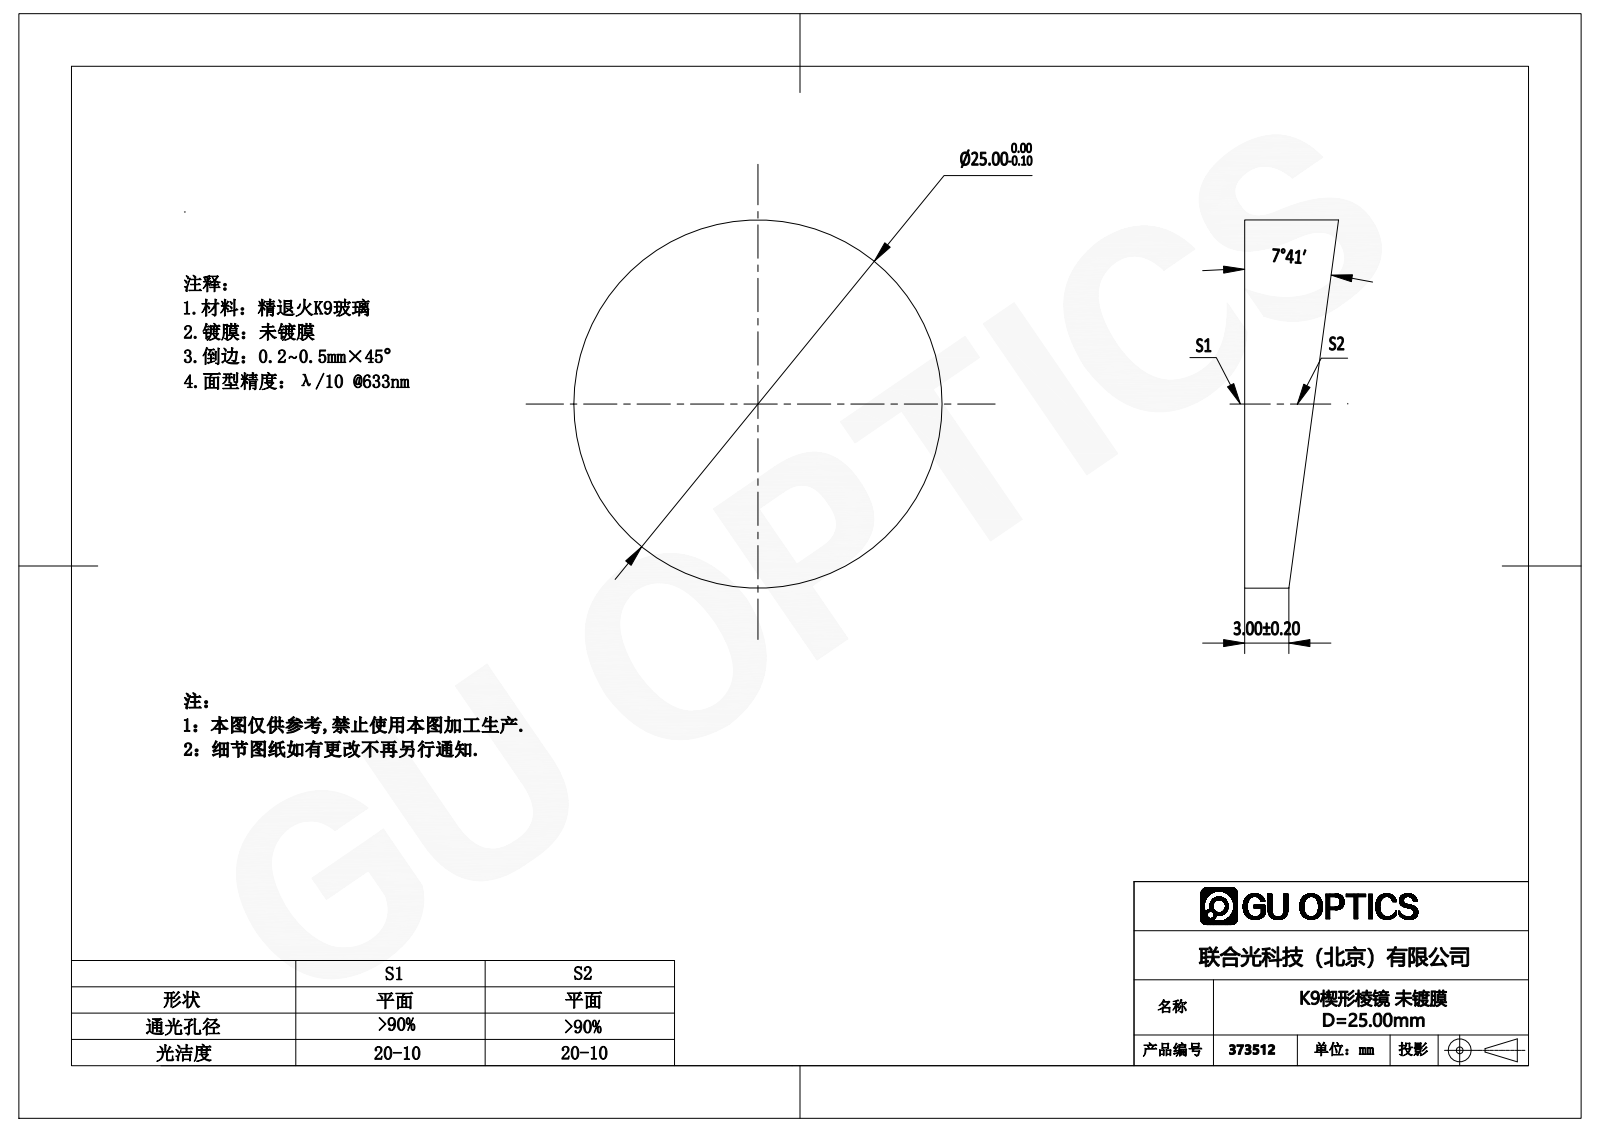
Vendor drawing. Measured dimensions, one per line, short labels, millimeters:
name: 373503
written by: SolidWorks 2016 (CONFIG_CONTROL_DESIGN)
unit: mm
bodies: 1 solid, 4 faces (2 planar, 2 cylindrical, 0 other)
size: 25 × 25 × 6.37
volume: 2 300 mm³; area: 1 354 mm²
bosses: 1× ⌀25
